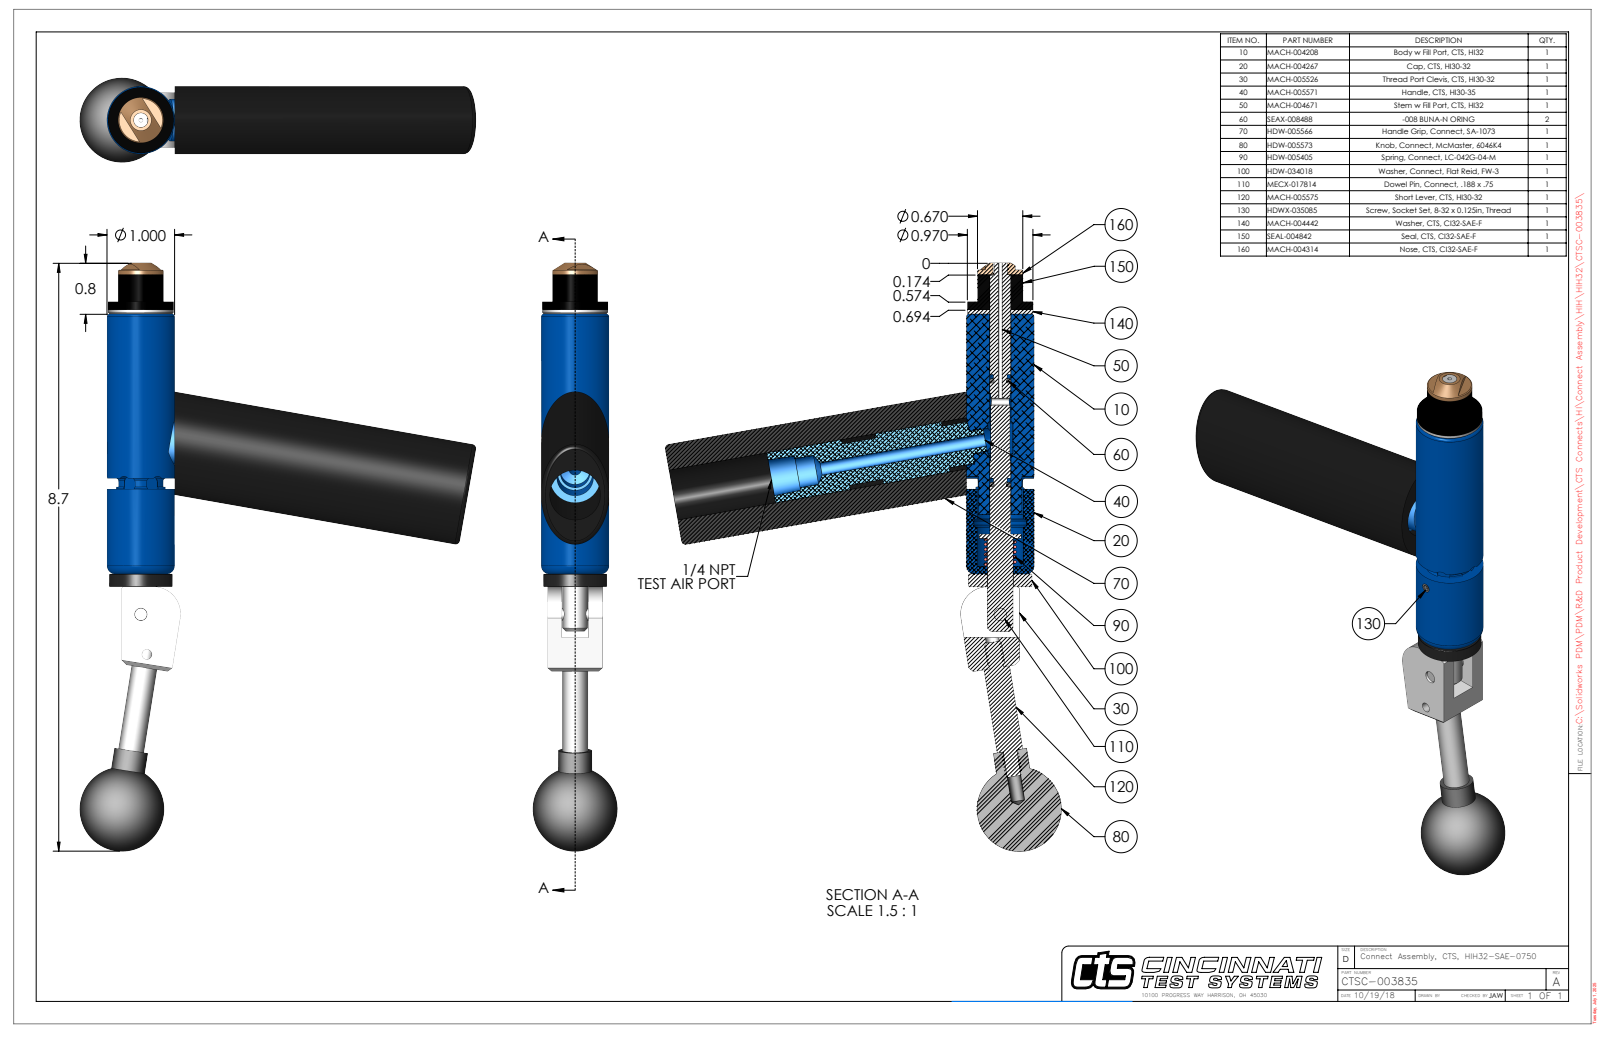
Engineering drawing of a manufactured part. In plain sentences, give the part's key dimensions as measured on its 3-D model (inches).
The part is named "CTSC-003835". Its 3-D file was written by "SolidWorks 2023 (AUTOMOTIVE_DESIGN)". It is 10 solids with 317 faces: 116 planar, 132 cylindrical and 69 other. Overall it measures 8.692 by 5.856 by 1.25 inches. Its volume is 9.456 cubic inches and its surface area 78.17 square inches. Round holes: 2 of diameter 0.201, 1 of diameter 0.063, 1 of diameter 0.109, 1 of diameter 0.136, 1 of diameter 0.15, 1 of diameter 0.187, 1 of diameter 0.189, 1 of diameter 0.213, 1 of diameter 0.31, 1 of diameter 0.314, 1 of diameter 0.316, 1 of diameter 0.385. Round bosses or shafts: 2 of diameter 0.25, 2 of diameter 0.201, 1 of diameter 1, 1 of diameter 0.97, 1 of diameter 0.936, 1 of diameter 0.75, 1 of diameter 0.67, 1 of diameter 0.62. Partial cylindrical surfaces (rounded edges, fillets, slot ends): 6 of radius 0.093, 2 of radius 0.029, 1 of radius 0.066, 1 of radius 0.325, 1 of radius 0.375, 1 of radius 0.4, 1 of radius 0.458. The main face-to-face distances are 0.06, 0.21, 0.602, 3.9, 3.841, 0.812, 4.088, 4.028, 0.187, 0.52. The hole center spacings are 0.599, 1.658, 2.252.
